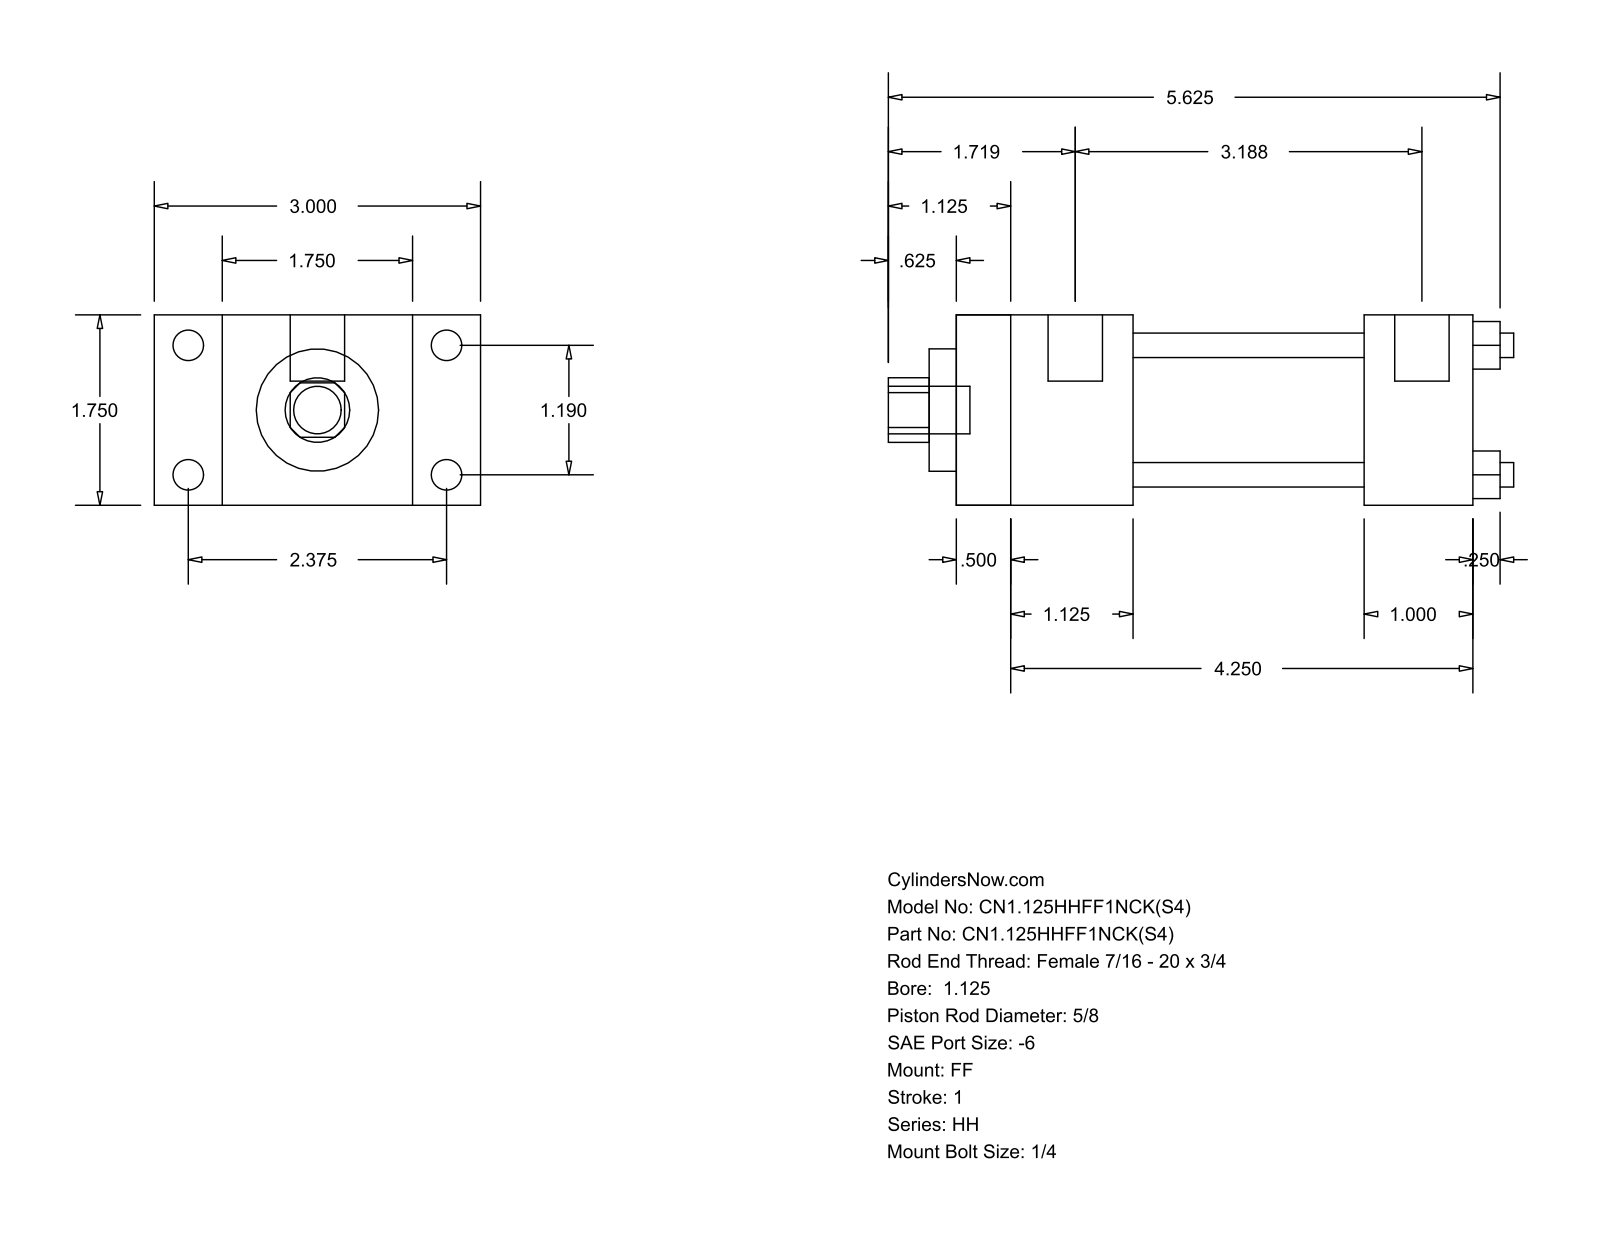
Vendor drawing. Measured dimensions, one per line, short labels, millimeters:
name: HH_FF__0112_0.625
written by: GSSL Pune (CONFIG_CONTROL_DESIGN)
unit: mm
bodies: 0 solids, 92 faces (64 planar, 28 cylindrical, 0 other)
size: 146.05 × 76.2 × 44.45
holes: 4× ⌀5.71, 1× ⌀15.88, 1× ⌀28.57, 1× ⌀34.92
bosses: 4× ⌀7.14, 4× ⌀5.56, 2× ⌀12.7, 1× ⌀11.11
rounds: 1× R7.54
face distances: 44.46, 120.65, 15.87, 12.69, 107.96, 60.33, 28.58, 41.27, 95.24, 82.55
hole spacings: 21.37, 30.22, 42.74
